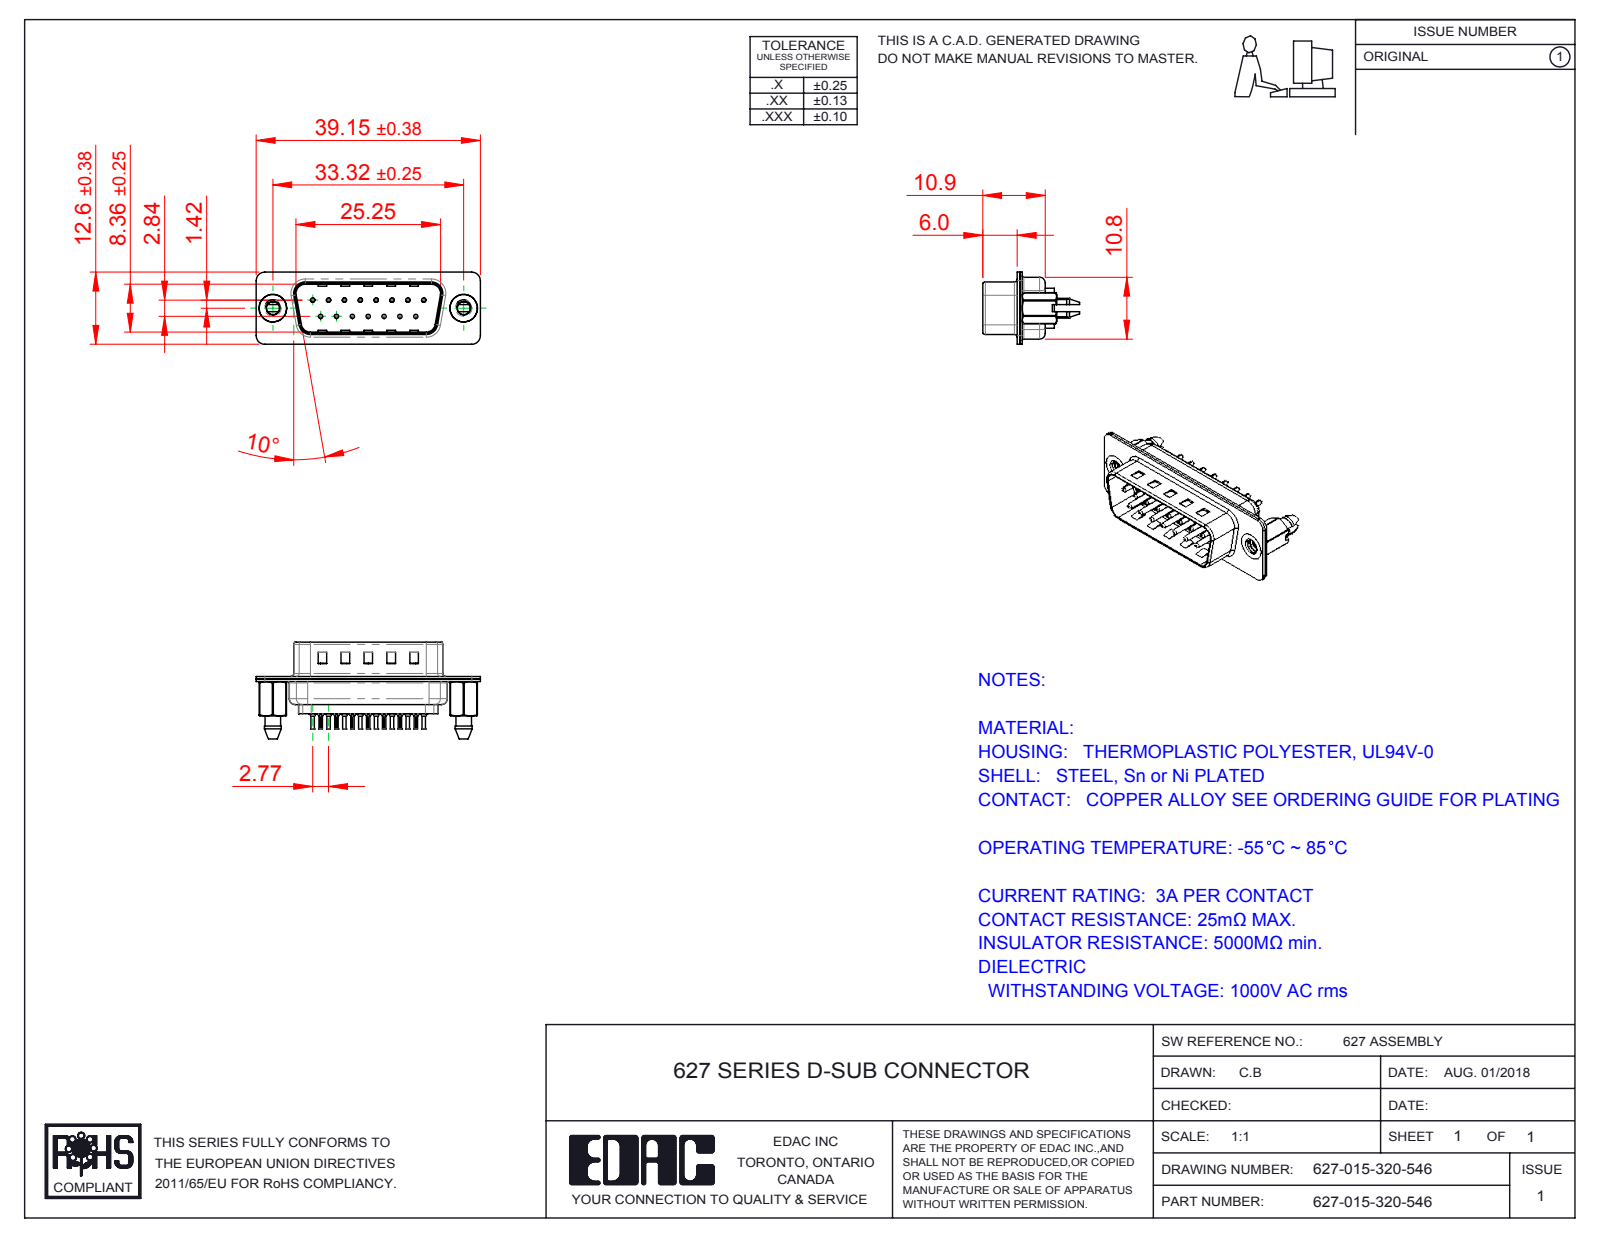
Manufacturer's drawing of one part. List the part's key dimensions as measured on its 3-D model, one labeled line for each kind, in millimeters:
Part name (STEP PRODUCT): 627 Contact Row 1_20L; 627 Contact Row 2_20L; 627-015-320-546; 627 4-40 Threaded Boardlock_LP (+3 more)
STEP written by: SolidWorks 2016 (CONFIG_CONTROL_DESIGN)
Units: millimetres
Bodies: 20 solids, 1884 faces (531 planar, 720 cylindrical, 633 other)
Overall size (bounding box): 39.15 × 16.9 × 12.6
Volume: 1 938 mm³ · Surface area: 5 593 mm²
Round holes (diameter × count): ⌀0.2 ×15, ⌀0.35 ×15, ⌀1.1 ×15, ⌀1.6 ×15, ⌀2.26 ×2, ⌀4 ×2, ⌀4.8 ×2
Round bosses / shafts (diameter × count): ⌀2 ×15, ⌀1.5 ×15, ⌀0.75 ×15, ⌀0.6 ×15, ⌀4.9 ×2
Partial cylindrical surfaces — rounded edges, fillets, slot ends (radius × count): R0.1 ×30, R1.5 ×18, R2 ×12, R1.6 ×10, R0.5 ×8, R0.25 ×4, R0.6 ×4, R0.65 ×4
Main face-to-face distances: 0.4, 0.45, 0.9, 0.82, 9.58, 8.76, 1.5, 1.4, 6.5, 5.6
Hole centre spacings: 3.16, 2.77, 5.54, 8.31, 11.08, 5.03, 5.04, 7.48
